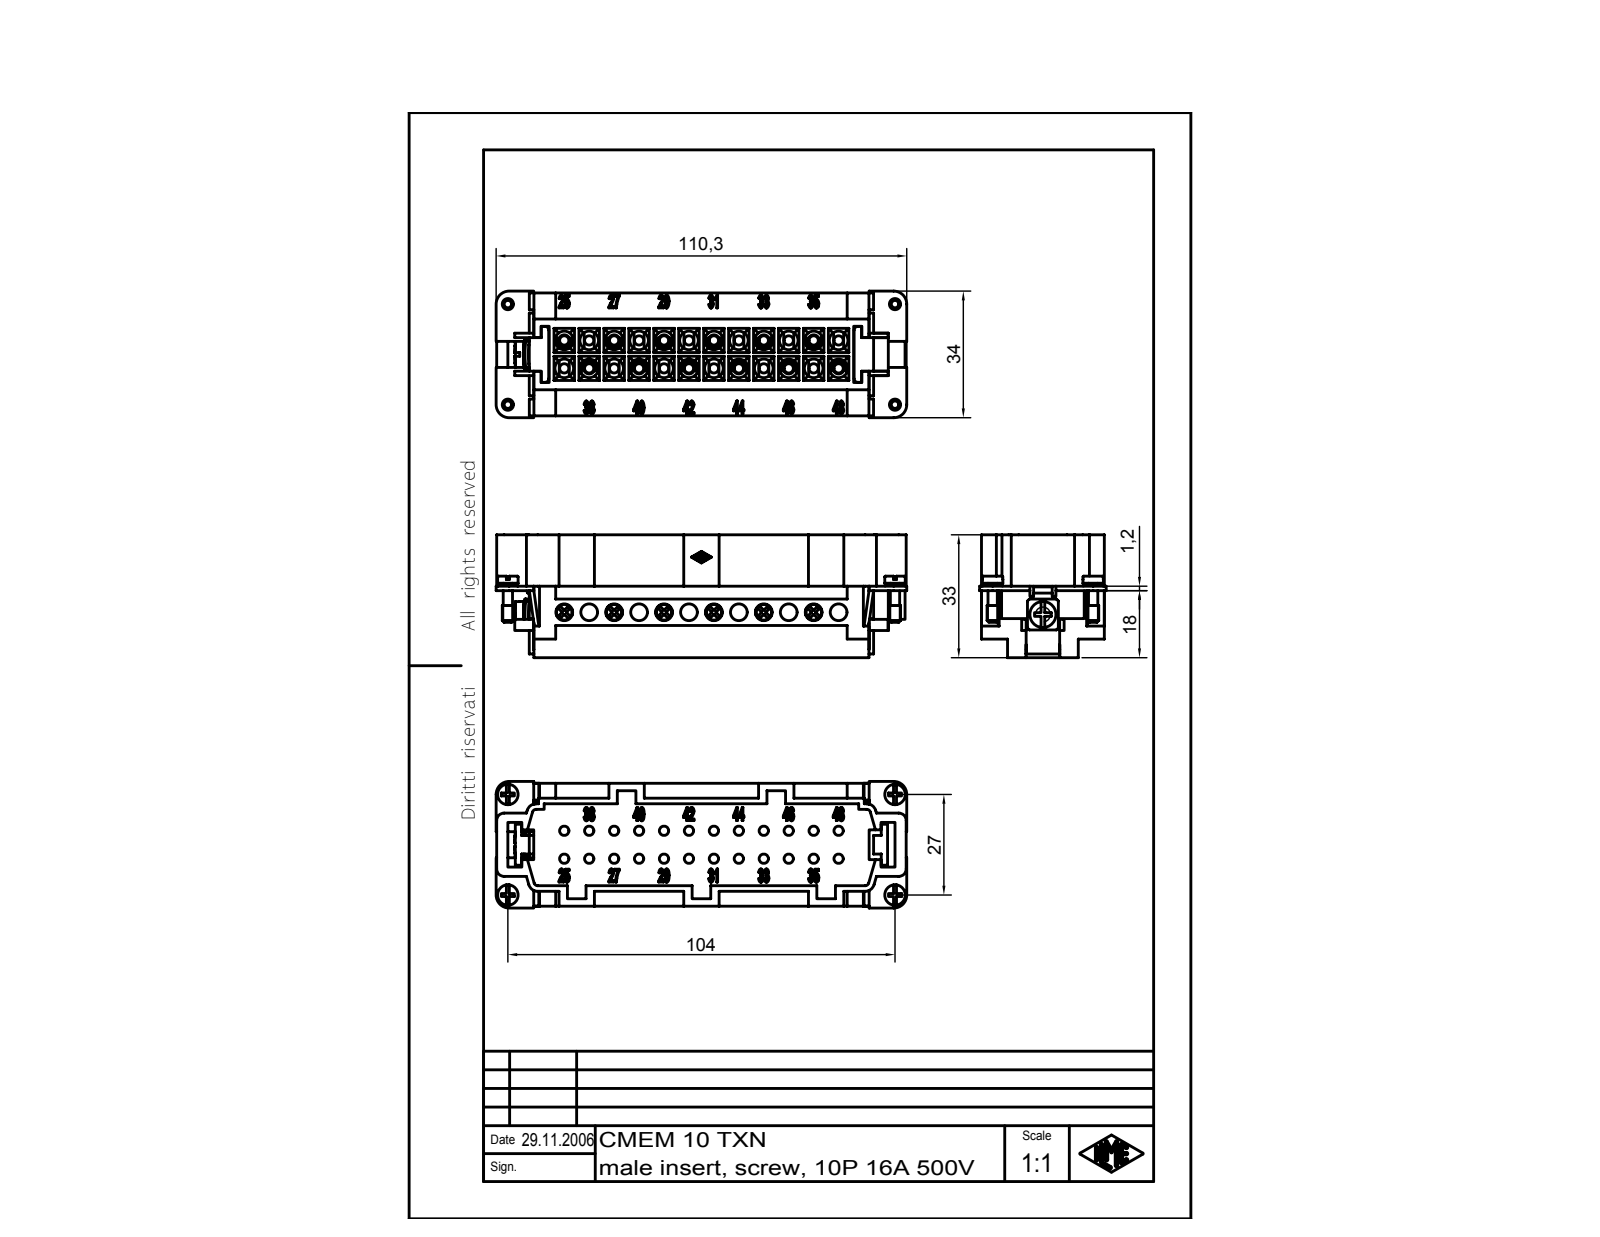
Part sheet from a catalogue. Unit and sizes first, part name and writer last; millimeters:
Units: millimetres
Overall size (bounding box): 110.3 × 34 × 33
Round holes (diameter × count): ⌀2.5 ×12, ⌀3 ×12, ⌀4.5 ×12, ⌀5 ×12, ⌀2.55 ×2
Round bosses / shafts (diameter × count): ⌀4.2 ×12, ⌀2.5 ×8, ⌀5.5 ×2, ⌀5.3 ×2, ⌀3 ×2, ⌀7 ×1
Partial cylindrical surfaces — rounded edges, fillets, slot ends (radius × count): R0.1 ×14, R2.1 ×12, R1 ×6, R2 ×6, R2.5 ×4, R3.5 ×2, R1.62 ×1, R5.5 ×1
Main face-to-face distances: 1.5, 22, 3, 20.5, 4, 7, 5.5, 29, 23.5, 26
Hole centre spacings: 6.7, 13.4, 20.1, 26.8, 10.06, 33.5, 15.36, 21.45
Volume: 44 016 mm³ · Surface area: 39 951 mm²
Bodies: 13 solids, 2161 faces (1046 planar, 311 cylindrical, 804 other)
Part name (STEP PRODUCT): CMEM 10 TXN
STEP written by: Autodesk Inventor 7 (AUTOMOTIVE_DESIGN)
